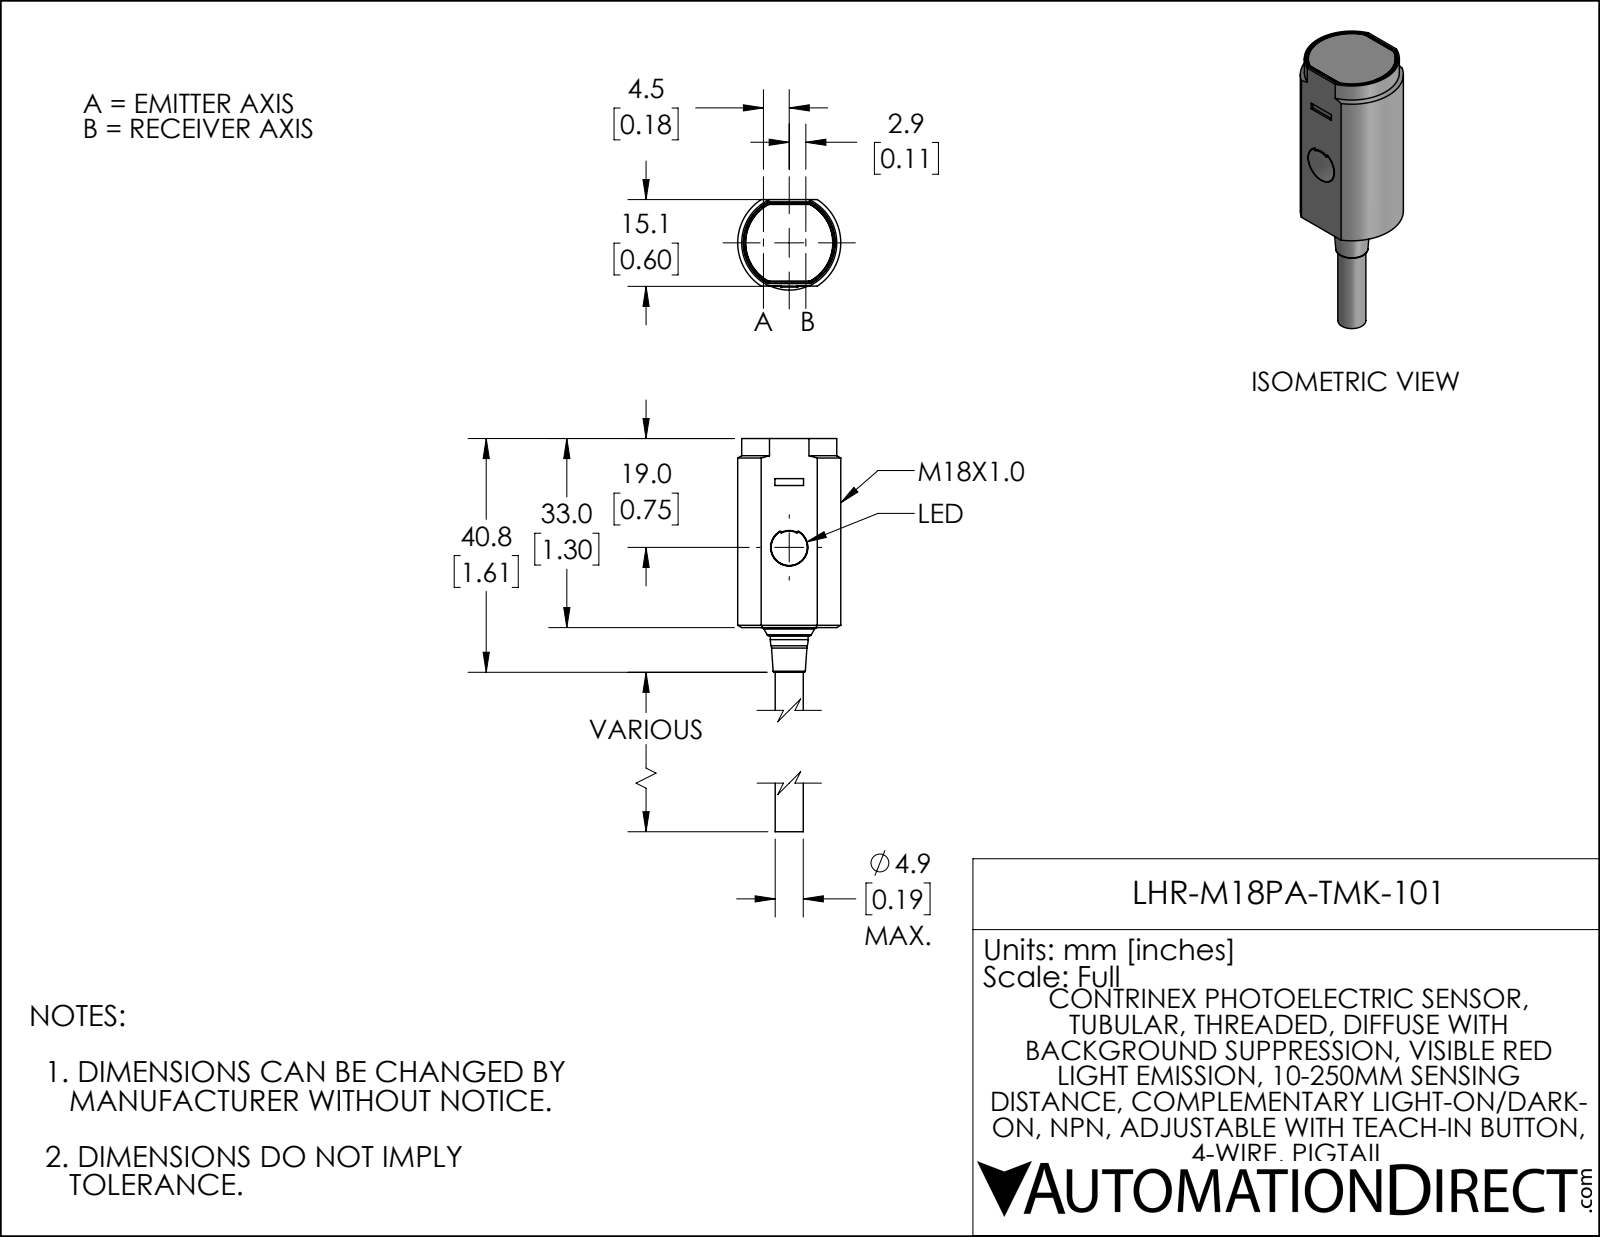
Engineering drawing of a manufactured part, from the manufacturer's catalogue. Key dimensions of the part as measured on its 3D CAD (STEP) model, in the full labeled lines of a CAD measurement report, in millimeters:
Part name (STEP PRODUCT): LHR-M18PA-TMK-101
STEP written by: SolidWorks 2021 (AUTOMOTIVE_DESIGN)
Units: millimetres
Bodies: 1 solid, 93 faces (39 planar, 41 cylindrical, 13 other)
Overall size (bounding box): 56 × 18 × 15.8
Volume: 8 210 mm³ · Surface area: 2 729 mm²
Round holes (diameter × count): ⌀6.5 ×1
Round bosses / shafts (diameter × count): ⌀6.6 ×1, ⌀4.9 ×1
Partial cylindrical surfaces — rounded edges, fillets, slot ends (radius × count): R0.2 ×8, R0.4 ×8, R0.7 ×8, R2.8 ×1, R2.9 ×1, R7.6 ×1, R7.7 ×1, R8 ×1
Main face-to-face distances: 15.1, 32.9, 33, 0.4, 56, 56, 23, 14.7, 0.4, 14.3
